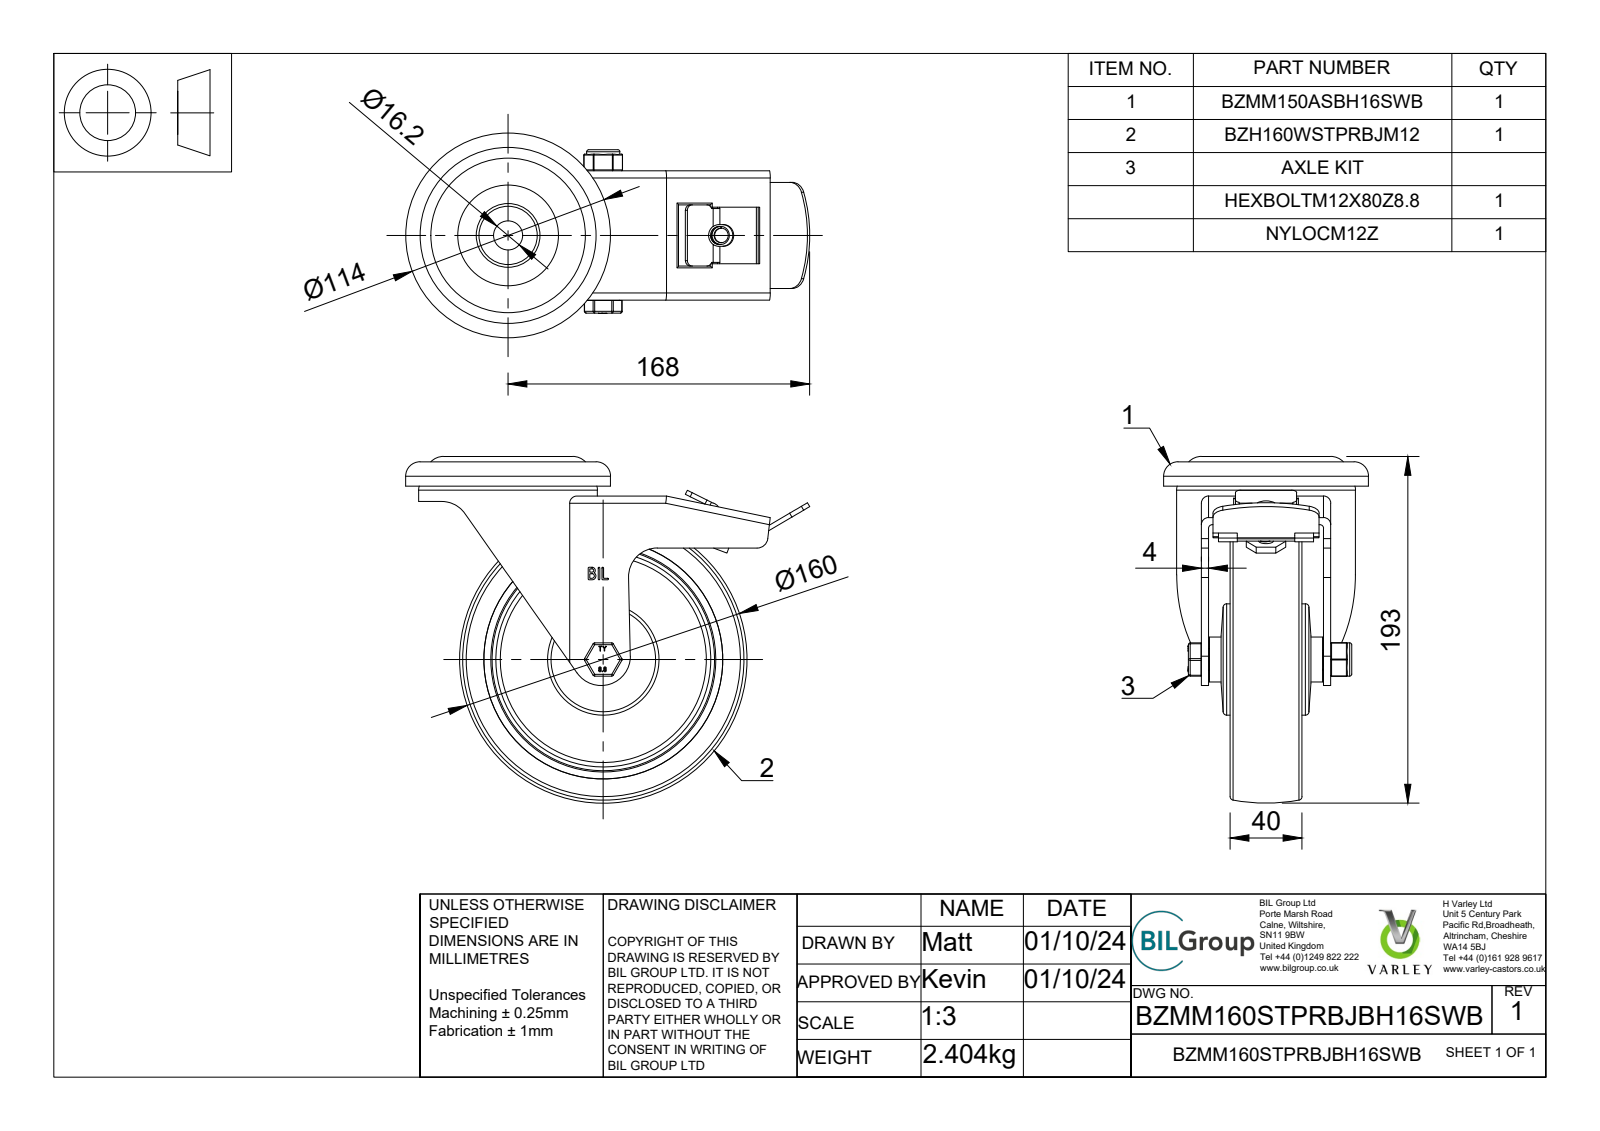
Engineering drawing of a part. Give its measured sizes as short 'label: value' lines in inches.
name: BZMM160STPRBJBH16SWB v2; BZMM150ASBH16SWB - 64 v1; ZINC PLATED, PRESSED STEEL HEAD; ZINC PLATED, PRESSED STEEL FORKS (+8 more)
written by: Autodesk Translation Framework v13.20.0.188 (AUTOMOTIVE_DESIGN)
unit: in
bodies: 26 solids, 920 faces (409 planar, 220 cylindrical, 291 other)
size: 8.858 × 7.598 × 4.488
volume: 43.3 in³; area: 443.3 in²
holes: 1× ⌀0.394, 1× ⌀0.404, 1× ⌀0.472, 1× ⌀0.48, 1× ⌀0.496, 1× ⌀0.551, 1× ⌀0.638, 1× ⌀0.787, 1× ⌀1.122, 1× ⌀1.213, 1× ⌀1.587, 1× ⌀1.594
bosses: 1× ⌀4.488, 1× ⌀3.917, 1× ⌀2.913, 1× ⌀2.441, 1× ⌀2.224, 1× ⌀1.89, 1× ⌀1.85, 1× ⌀1.606
rounds: 22× R0.02, 18× R0.039, 8× R0.079, 4× R0.118, 4× R0.157, 3× R0.236, 3× R0.315, 2× R0.63
face distances: 0.915, 0.659, 0.157, 0.472, 1.132, 1.388, 2.047, 0.256, 0.039, 1.575
